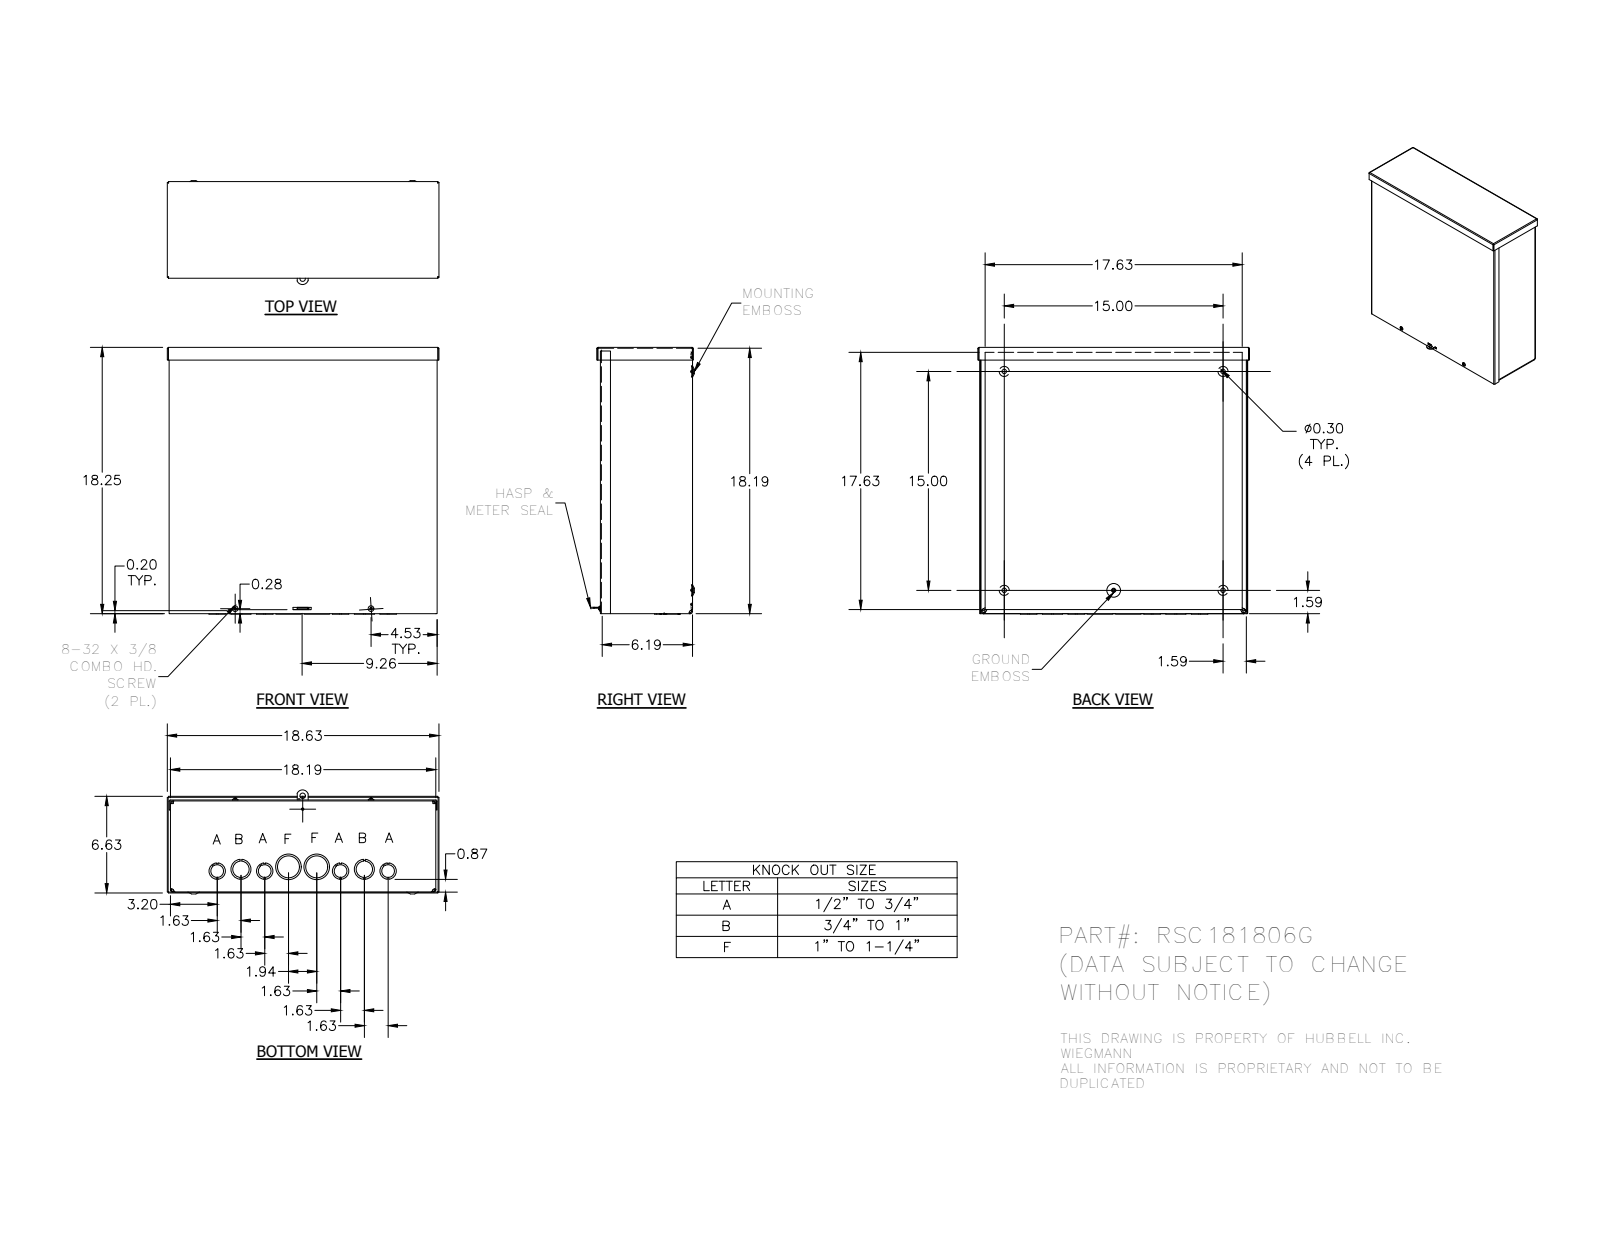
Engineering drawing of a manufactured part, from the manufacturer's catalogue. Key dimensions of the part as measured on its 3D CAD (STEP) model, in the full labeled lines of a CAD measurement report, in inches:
Part name (STEP PRODUCT): RSC181806G_WRAP; RSC1818G_LID; RSC1806G_CAP; 3183 (+4 more)
STEP written by: Autodesk Inventor 2014 (AUTOMOTIVE_DESIGN)
Units: inches
Bodies: 7 solids, 619 faces (304 planar, 171 cylindrical, 144 other)
Overall size (bounding box): 18.625 × 18.28 × 7.125
Volume: 85.56 in³ · Surface area: 2 782 in²
Round holes (diameter × count): ⌀1.125 ×6, ⌀0.3 ×4, ⌀0.313 ×4, ⌀0.875 ×4, ⌀0.125 ×2, ⌀0.148 ×2, ⌀1.375 ×2, ⌀1.5 ×2, ⌀1.75 ×2, ⌀0.156 ×1, ⌀0.165 ×1, ⌀0.375 ×1
Round bosses / shafts (diameter × count): ⌀0.384 ×2, ⌀0.164 ×2, ⌀0.228 ×1
Partial cylindrical surfaces — rounded edges, fillets, slot ends (radius × count): R0.01 ×15, R0.031 ×8, R0.093 ×8, R0.125 ×8, R0.187 ×8, R0.031 ×5, R0.021 ×4, R0.055 ×4
Main face-to-face distances: 0.062, 18.126, 6.249, 6.187, 0.063, 6.312, 6.25, 0.062, 18.188, 0.124
Hole centre spacings: 1.635, 15, 8.46, 1.656, 3.26, 3.264, 3.582, 4.898
